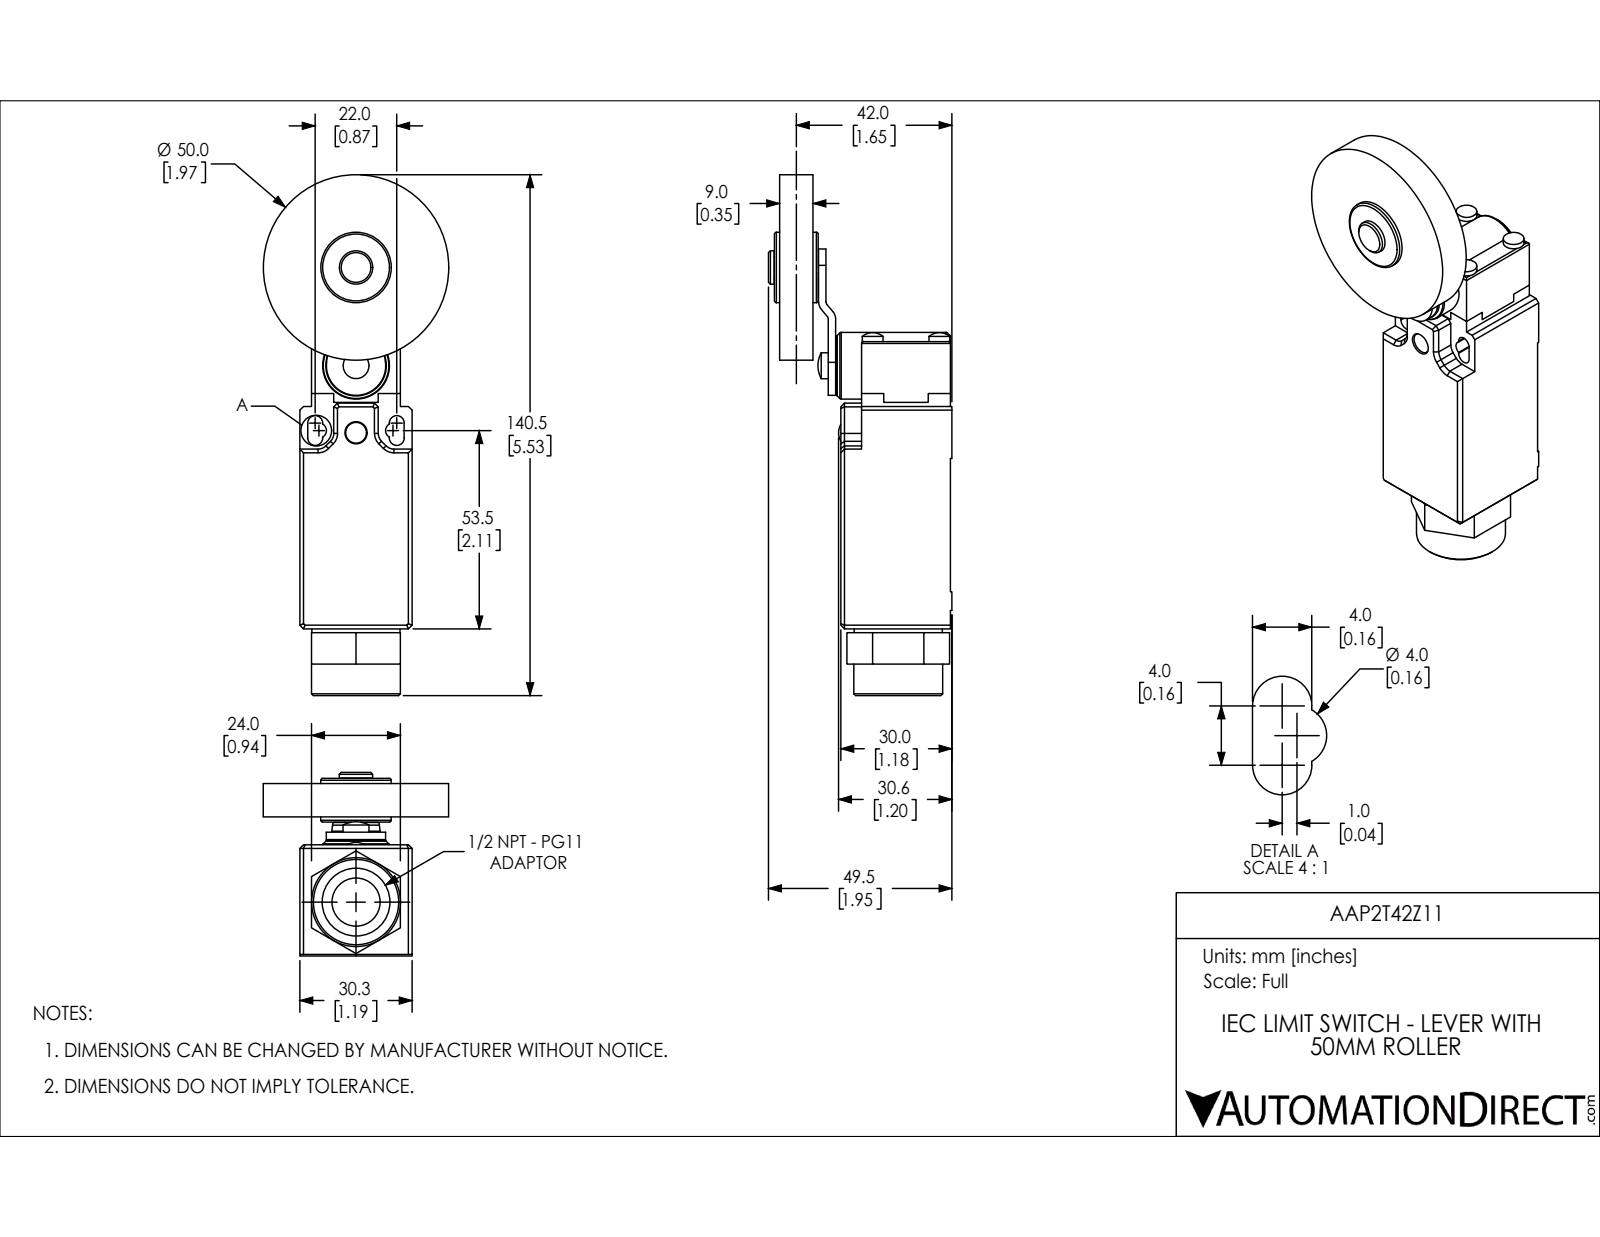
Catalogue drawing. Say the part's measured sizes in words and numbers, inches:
The part is named "AAP2T42Z11". Its 3-D file was written by "SolidWorks 2018 (AUTOMOTIVE_DESIGN)". It is 5 solids with 269 faces: 134 planar, 95 cylindrical and 40 other. Overall it measures 5.531 by 1.969 by 1.949 inches. Its volume is 5.319 cubic inches and its surface area 38.27 square inches. Round holes: 1 of diameter 0.236, 1 of diameter 0.512, 1 of diameter 0.669, 1 of diameter 0.72, 1 of diameter 0.74, 1 of diameter 0.748. Round bosses or shafts: 5 of diameter 0.22, 1 of diameter 1.969, 1 of diameter 0.945, 1 of diameter 0.937, 1 of diameter 0.748, 1 of diameter 0.724, 1 of diameter 0.709, 1 of diameter 0.587. Partial cylindrical surfaces (rounded edges, fillets, slot ends): 6 of radius 0.079, 6 of radius 0.118, 4 of radius 0.02, 2 of radius 0.039, 1 of radius 0.197, 1 of radius 0.315, 1 of radius 0.394, 1 of radius 0.4. The main face-to-face distances are 0.354, 0.65, 1.461, 1.815, 1.193, 1.165, 0.295, 0.945, 0.124, 1.069.
